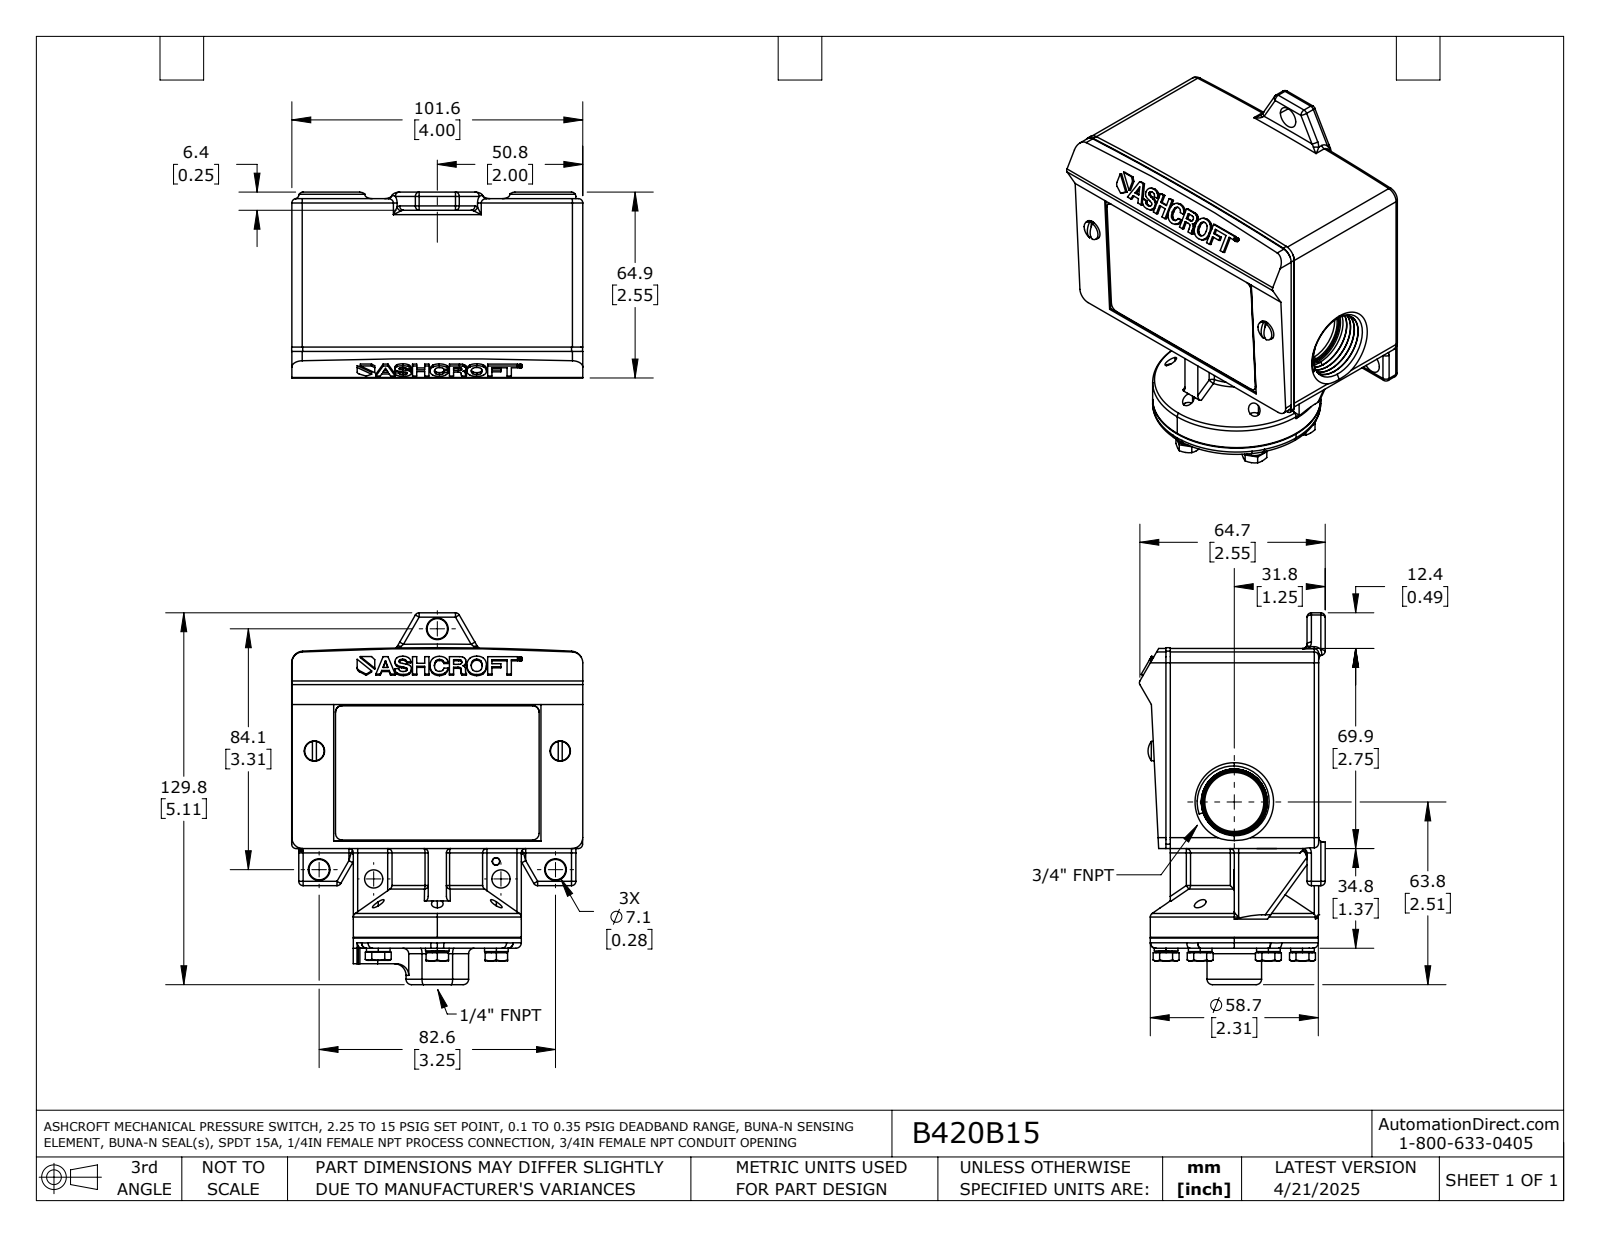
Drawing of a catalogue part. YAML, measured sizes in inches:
part_name: "B420B15"
step_written_by: "SolidWorks 2021 (AUTOMOTIVE_DESIGN)"
units: inches
bodies: {solids: 2, faces: 1259, planar: 345, cylindrical: 472, other: 442}
overall_size: [5.111, 4.003, 2.555]
volume: 28.57
surface_area: 84.51
round_holes:
  - {diameter: 0.161, count: 6}
  - {diameter: 0.192, count: 5}
  - {diameter: 0.209, count: 5}
  - {diameter: 0.187, count: 4}
  - {diameter: 0.28, count: 2}
  - {diameter: 0.455, count: 1}
  - {diameter: 0.812, count: 1}
round_bosses_or_shafts:
  - {diameter: 0.325, count: 6}
  - {diameter: 0.278, count: 6}
  - {diameter: 0.19, count: 5}
  - {diameter: 0.27, count: 2}
  - {diameter: 0.25, count: 2}
  - {diameter: 2.31, count: 1}
partial_cylinders:
  - {radius: 0.06, count: 92}
  - {radius: 0.03, count: 5}
  - {radius: 0.075, count: 4}
  - {radius: 0.09, count: 4}
  - {radius: 0.15, count: 4}
  - {radius: 0.01, count: 2}
  - {radius: 0.094, count: 2}
  - {radius: 0.16, count: 2}
face_to_face_distances: [4, 0.015, 1.37, 0.09, 3.91, 0.44, 3.56, 3.47, 0.35, 0.845]
hole_center_spacings: [0.937, 1.624, 1.875, 0.938, 3.38]
